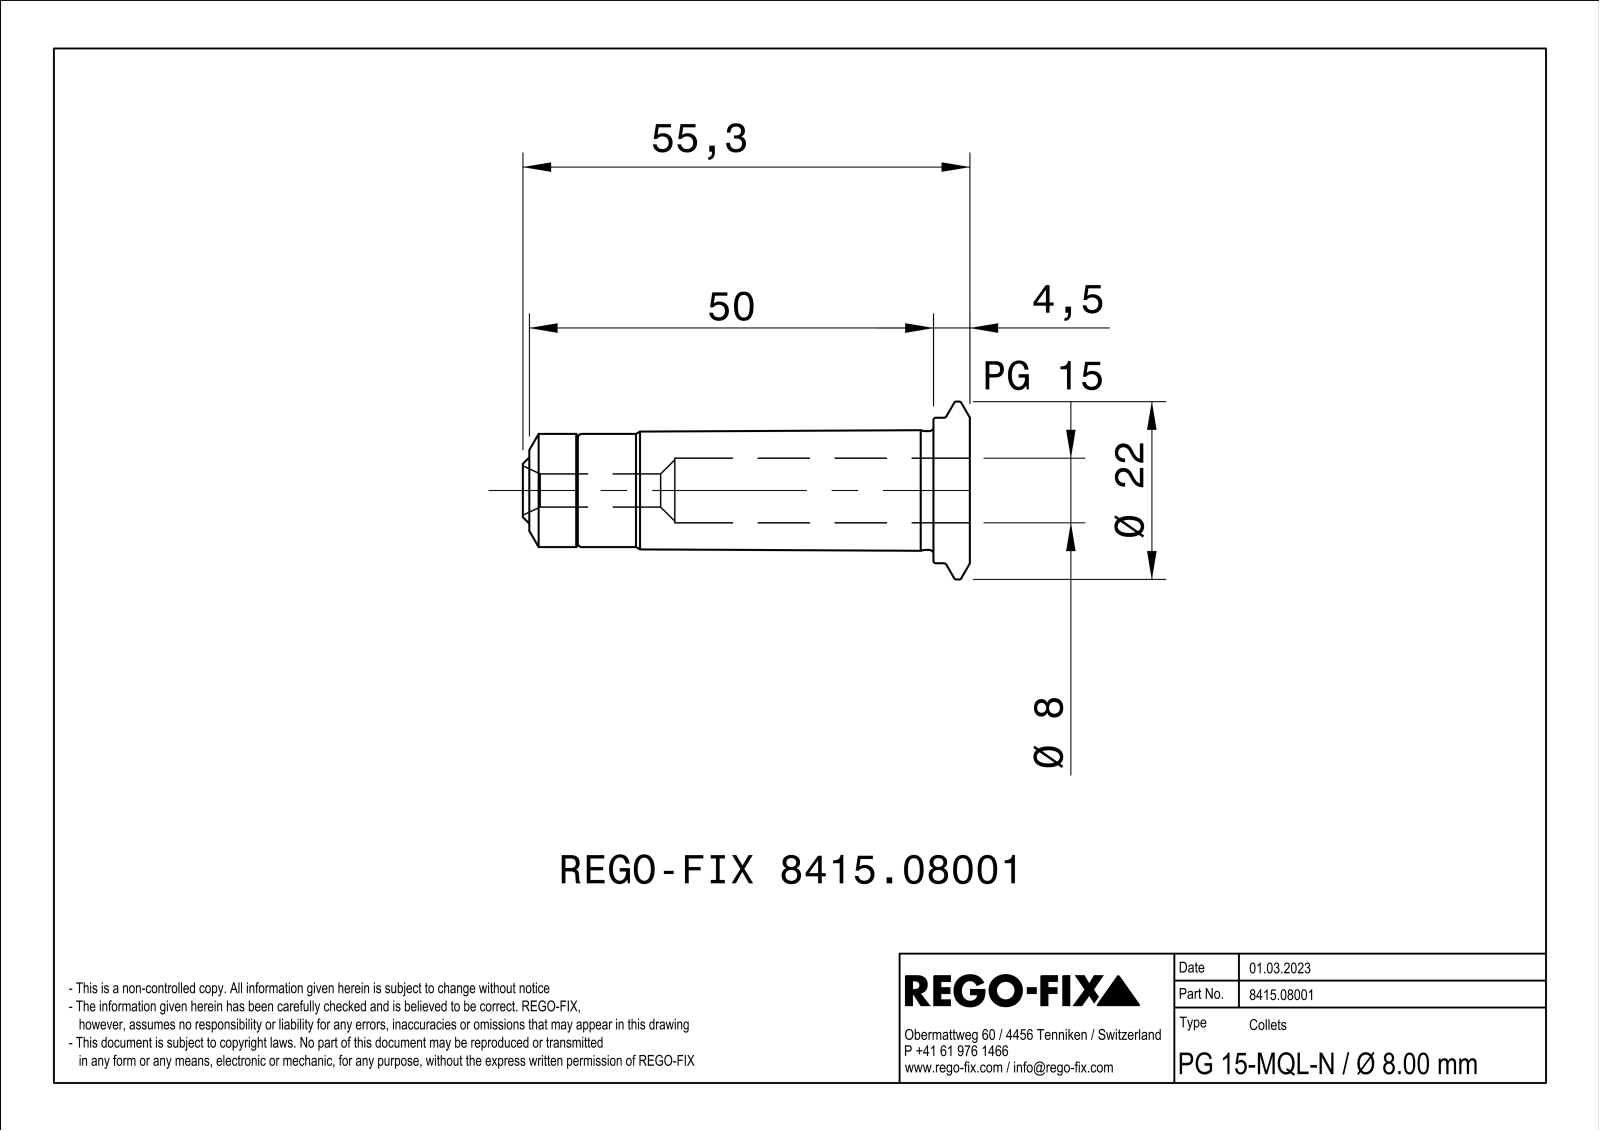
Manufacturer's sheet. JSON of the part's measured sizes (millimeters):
{"part_name": "NOCUT", "step_written_by": "SIEMENS PLM Software Solid Edge ST10 (AUTOMOTIVE_DESIGN)", "units": "millimeters", "bodies": {"solids": 2, "faces": 78, "planar": 16, "cylindrical": 17, "other": 45}, "overall_size": [55.3, 22, 21.99], "volume_mm3": 7653, "surface_area_mm2": 5866, "round_holes": [[4.1, 1], [8, 1], [10.92, 1], [12.2, 1]], "round_bosses_or_shafts": [[22, 1], [18, 1], [14.7, 1], [14, 1], [13, 1]], "face_to_face_distances": [1, 6, 48.5, 54.5, 12, 4.5, 44, 50, 42.5, 38]}
